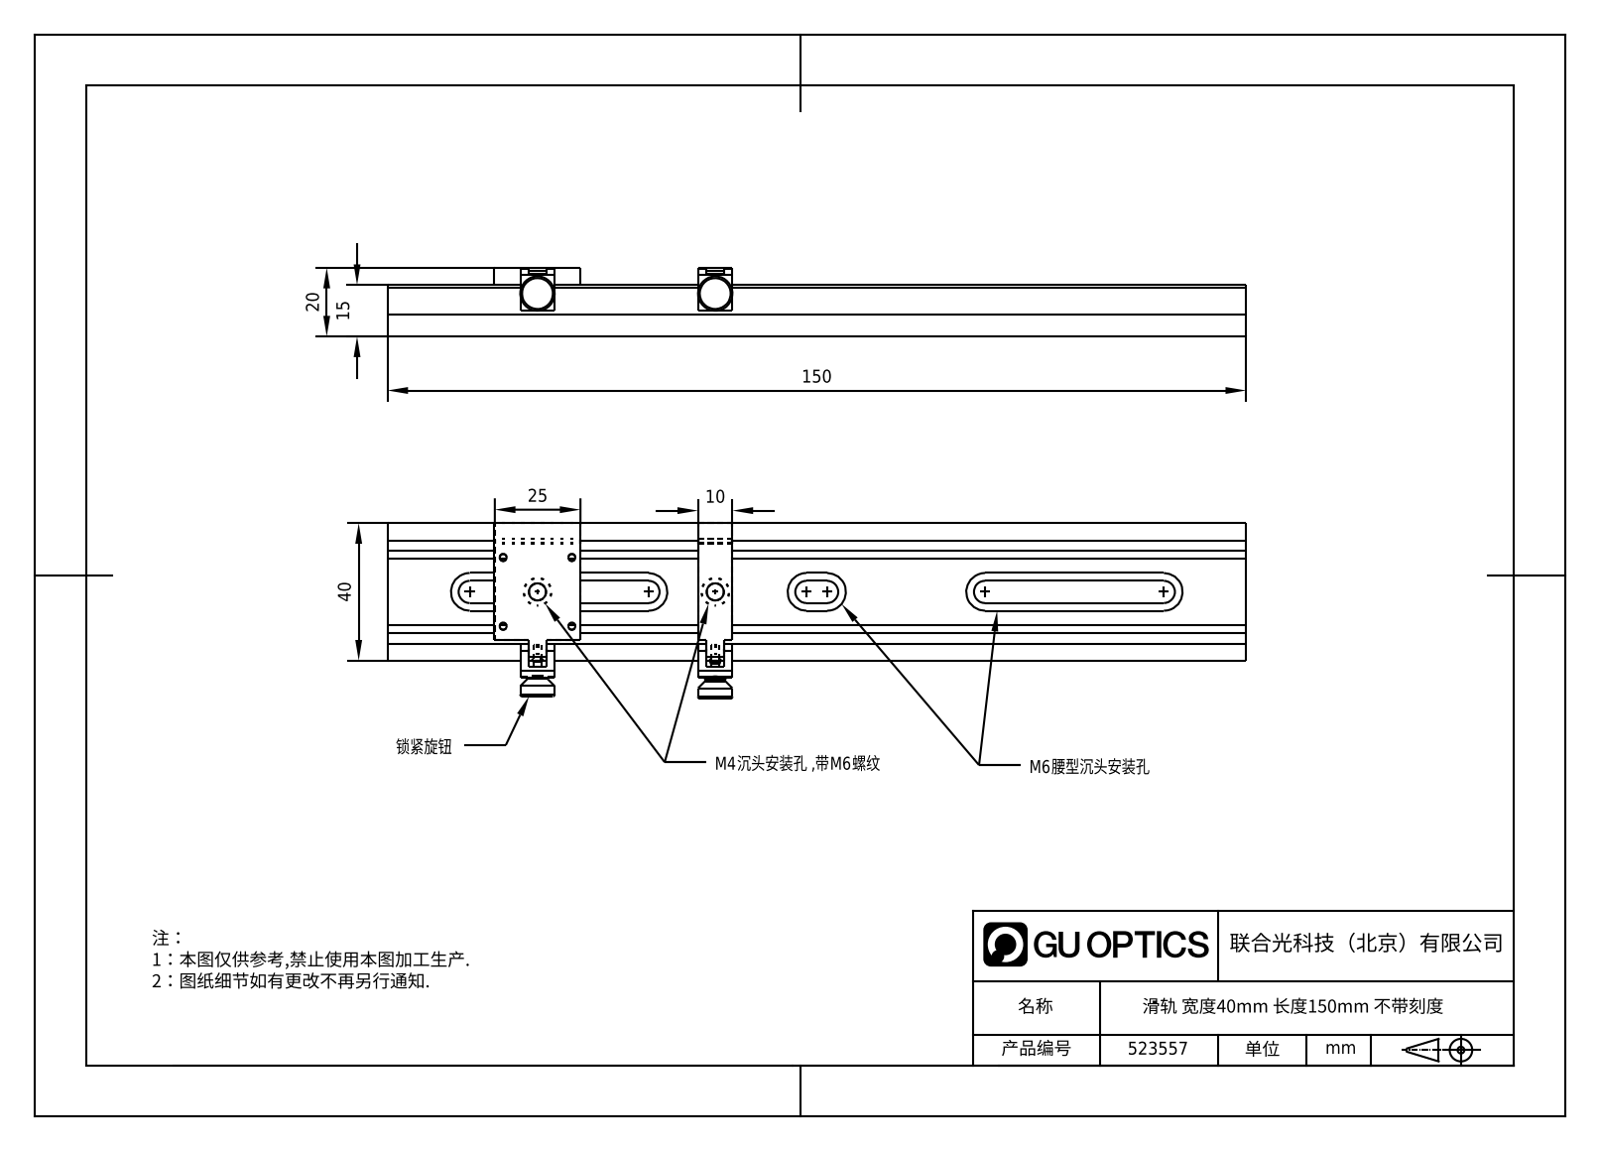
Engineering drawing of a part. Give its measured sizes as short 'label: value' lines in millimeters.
name: 4.2.1.3_H40G-150
written by: SolidWorks 2021 (CONFIG_CONTROL_DESIGN)
unit: mm
bodies: 0 solids, 157 faces (92 planar, 51 cylindrical, 14 other)
size: 150 × 51.03 × 20
holes: 4× ⌀2.05, 2× ⌀5, 2× ⌀8, 1× ⌀1.5
bosses: 2× ⌀10, 2× ⌀6
rounds: 6× R3.25, 6× R5.5, 1× R2.5, 1× R4.5, 1× R12.5
face distances: 6, 14.5, 0.5, 5, 15, 8.5, 6.5, 19.5, 20, 13.5
hole spacings: 14.14, 20, 28.28, 64.38, 84.2, 73.6
